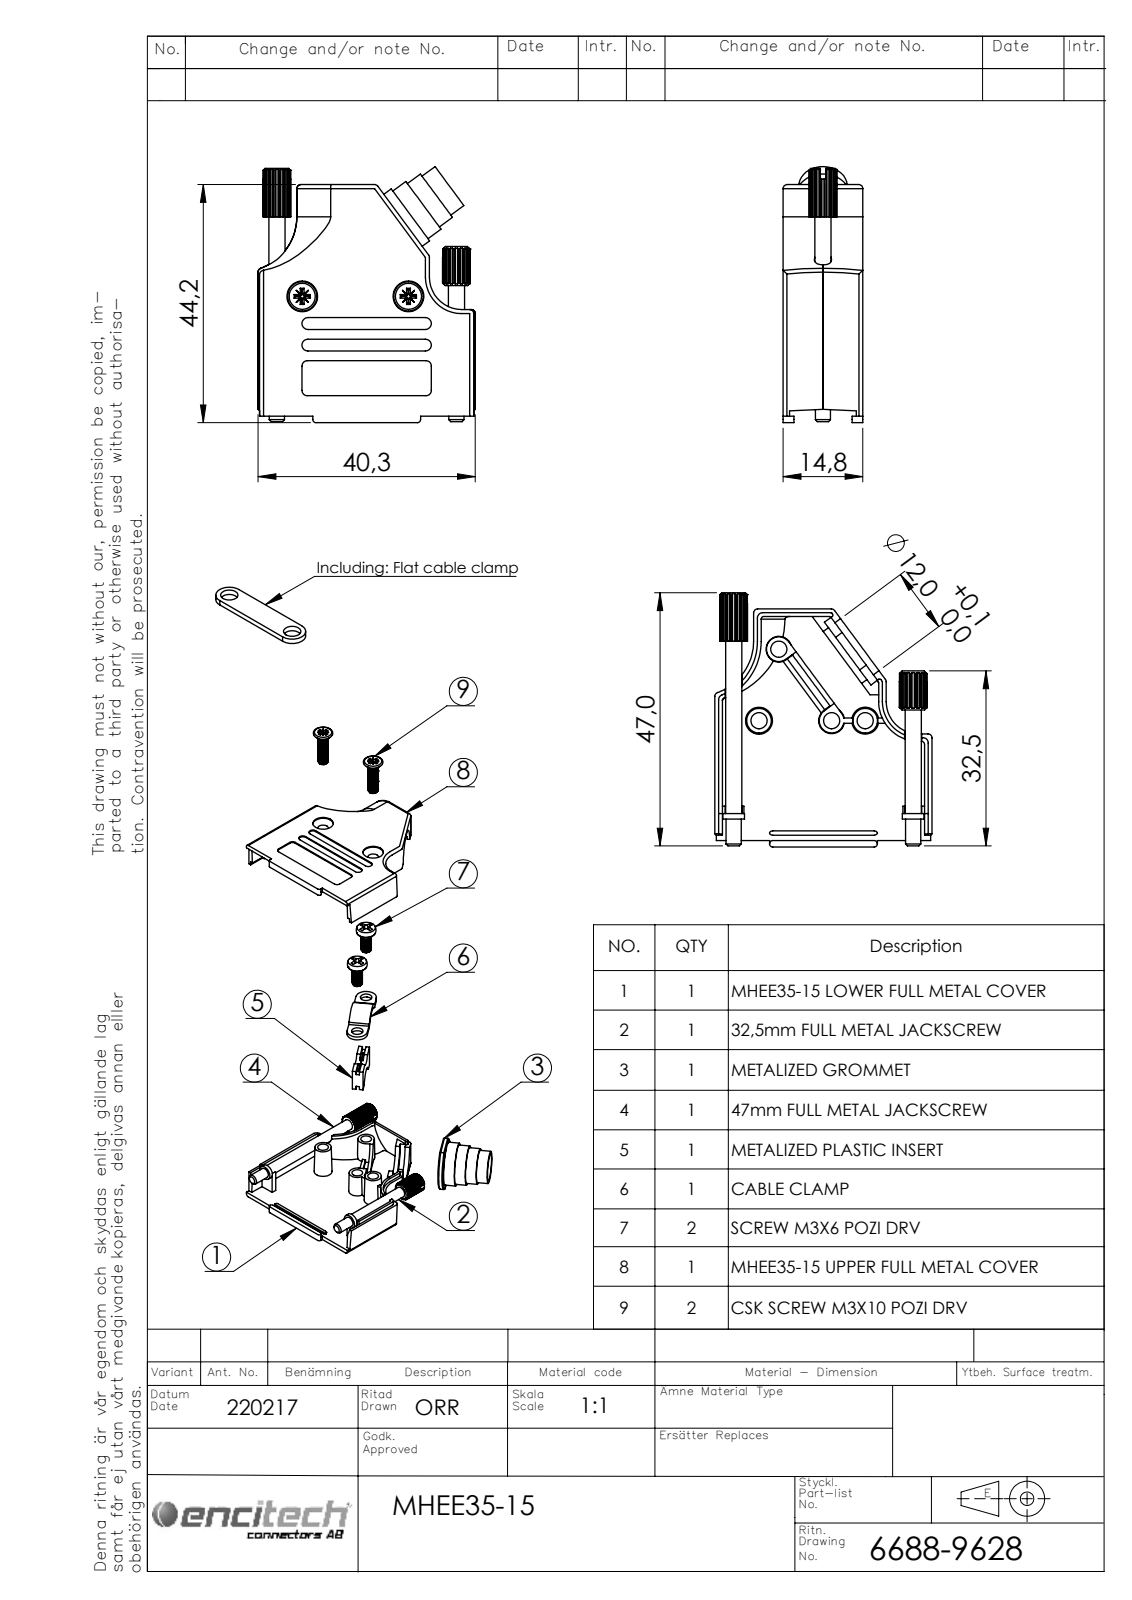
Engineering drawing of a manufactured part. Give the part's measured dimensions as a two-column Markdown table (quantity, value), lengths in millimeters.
| quantity | value |
| --- | --- |
| part name | 6855-0117-03; 6560-0140-12; 6830-0109-01; 6805-0139-02 (+6 more) |
| STEP written by | SolidWorks 2021 (AUTOMOTIVE_DESIGN) |
| units | millimeters |
| bodies | 11 solids, 875 faces (428 planar, 320 cylindrical, 127 other) |
| overall size | 47.54 × 40.3 × 14.8 |
| volume | 7 134 mm³ |
| surface area | 13 154 mm² |
| round holes (diameter × count) | 3 × 4, 3.2 × 4, 4.8 × 2, 5.7 × 2, 7.5 × 1, 8.5 × 1, 9.5 × 1, 10.5 × 1, 12 × 1 |
| round bosses / shafts (diameter × count) | 2.9 × 4, 4 × 2, 3 × 2, 2.8 × 2, 11 × 1, 10 × 1, 9 × 1 |
| partial cylindrical surfaces (radius × count) | 0.75 × 16, 0.3 × 9, 1 × 9, 0.1 × 8, 1.1 × 4, 0.38 × 3, 0.5 × 3, 0.6 × 2 |
| main face-to-face distances | 1.2, 13.6, 12.4, 14.8, 6.2, 13.3, 14.5, 0.9, 7.1, 7.4 |
| hole center spacings | 6.23, 13.47, 13.77, 16.5, 19.7, 20.81, 33.3 |
